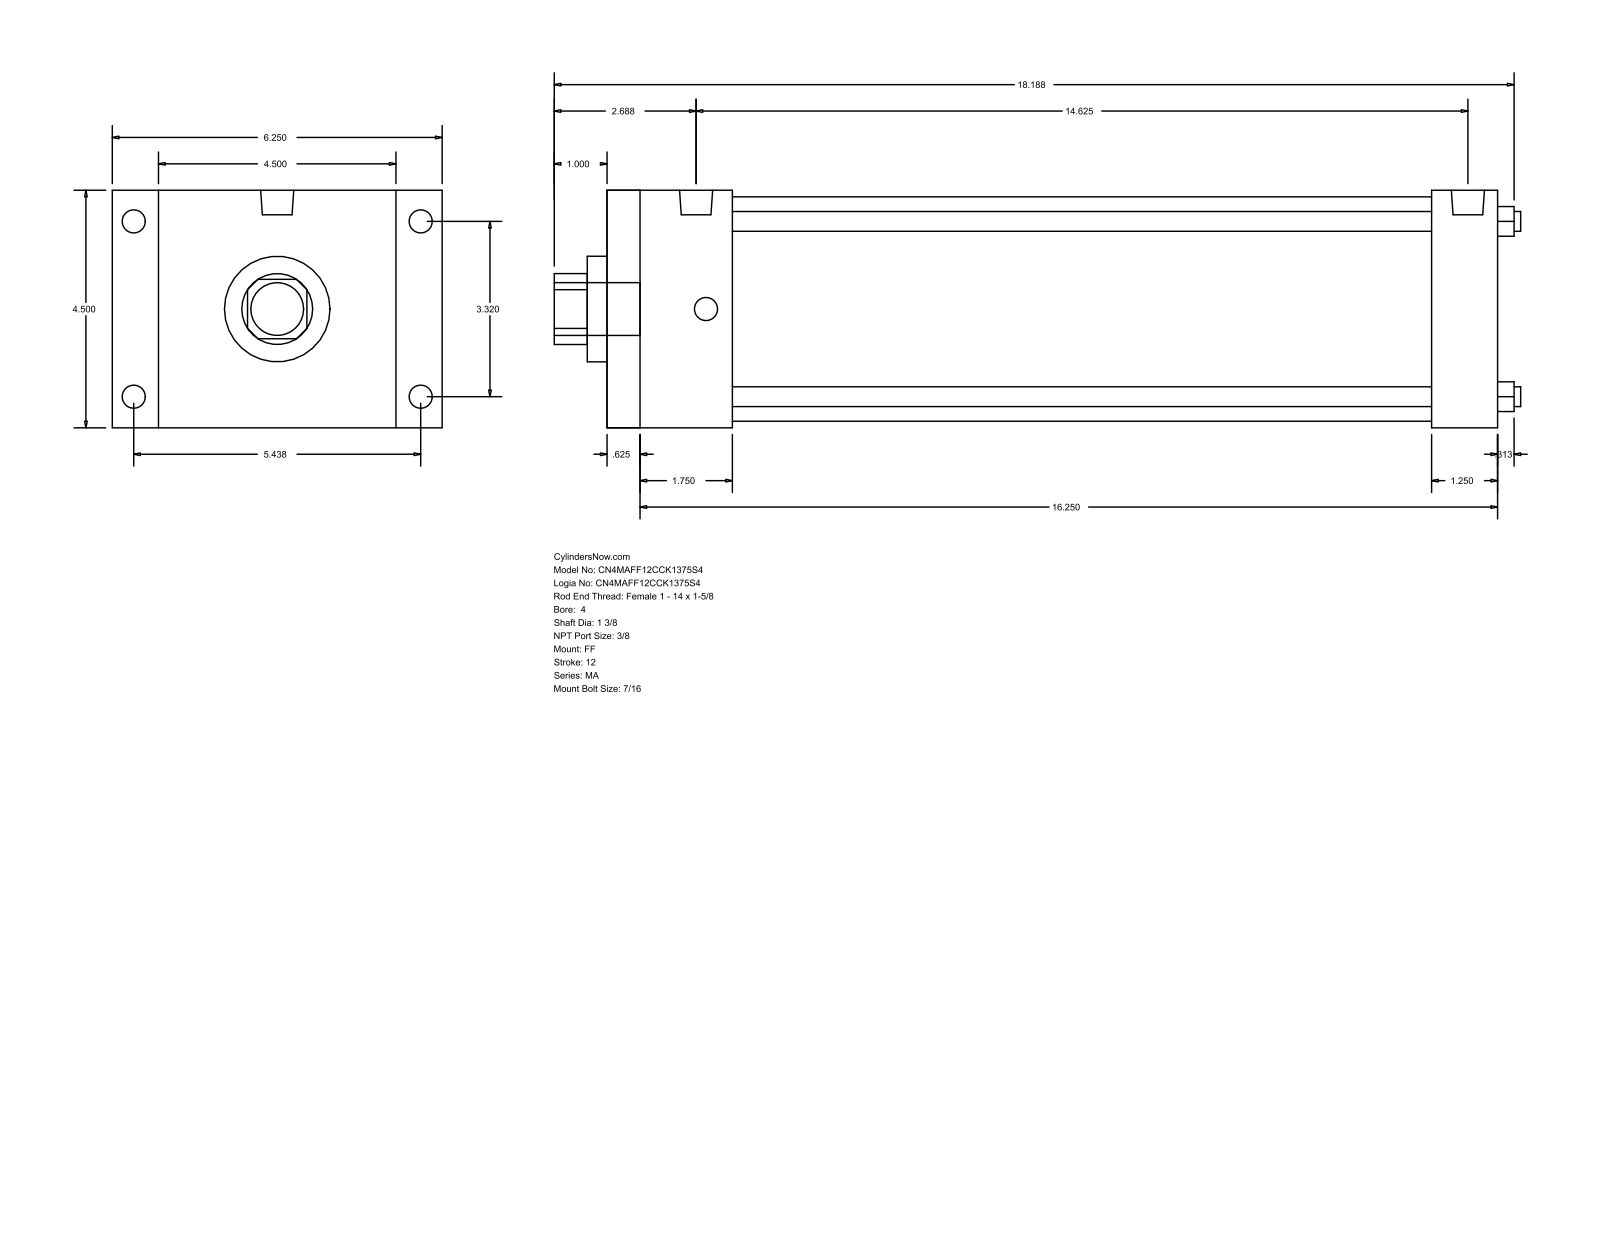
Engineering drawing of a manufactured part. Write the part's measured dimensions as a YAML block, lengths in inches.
part_name: "MA_FF__0400_1.375"
step_written_by: "GSSL Pune (CONFIG_CONTROL_DESIGN)"
units: inches
bodies: {solids: 0, faces: 92, planar: 64, cylindrical: 28, other: 0}
overall_size: [18.313, 6.25, 4.5]
round_holes:
  - {diameter: 0.375, count: 4}
  - {diameter: 1.375, count: 1}
  - {diameter: 2, count: 1}
  - {diameter: 4.25, count: 1}
round_bosses_or_shafts:
  - {diameter: 0.437, count: 8}
  - {diameter: 0.627, count: 2}
  - {diameter: 1, count: 1}
partial_cylinders:
  - {radius: 0.672, count: 1}
face_to_face_distances: [4.5, 16.875, 0.625, 16.25, 0.875, 5.375, 15.625, 15, 1.25, 2.375]
hole_center_spacings: [2.347, 3.32, 4.695]
